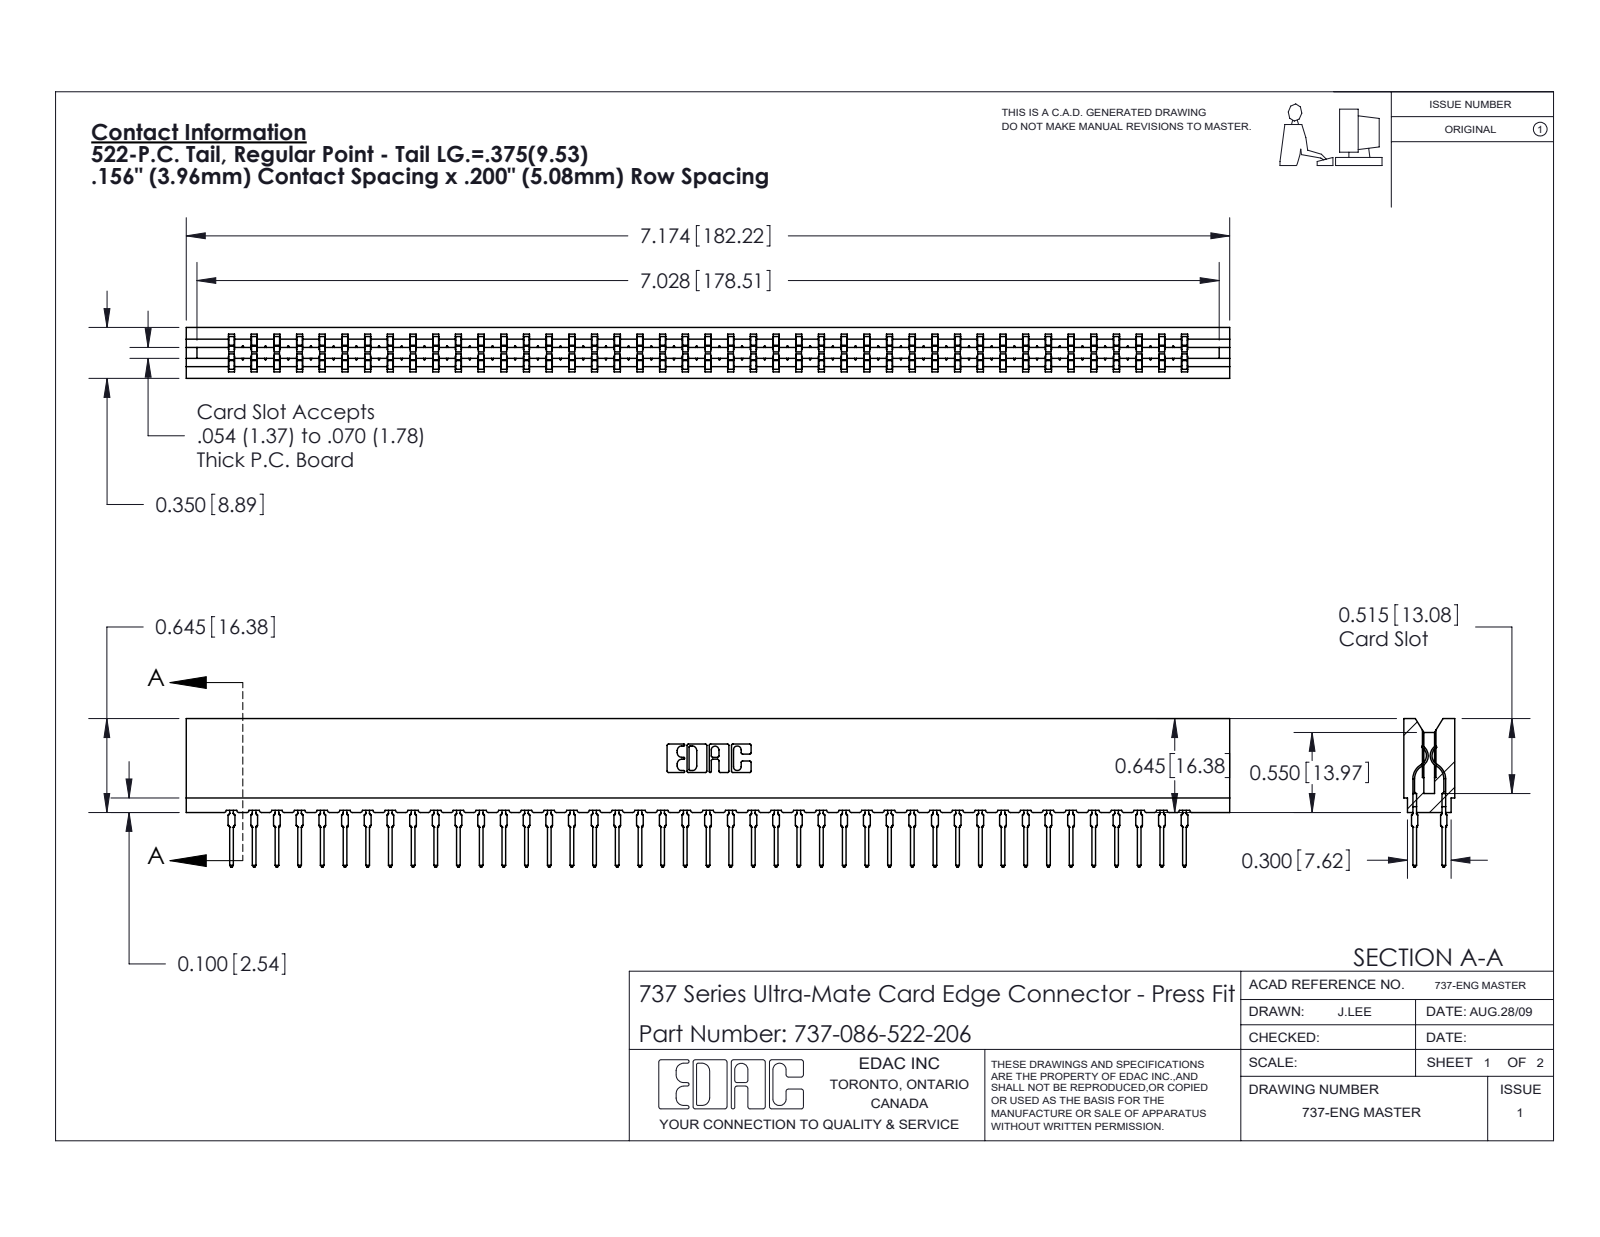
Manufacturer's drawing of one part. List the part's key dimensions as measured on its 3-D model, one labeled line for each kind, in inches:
Part name (STEP PRODUCT): 745-292-001_522; 737-086-522-206; 737 Part_Insulator Option - 06
STEP written by: SolidWorks 2020 (CONFIG_CONTROL_DESIGN)
Units: inches
Bodies: 87 solids, 7835 faces (4054 planar, 1545 cylindrical, 2236 other)
Overall size (bounding box): 7.174 × 1.021 × 0.35
Volume: 1.103 in³ · Surface area: 41.29 in²
Partial cylindrical surfaces — rounded edges, fillets, slot ends (radius × count): R0.021 ×172, R0.015 ×86, R0.01 ×22, R0.005 ×8, R0.011 ×8, R0.007 ×6, R0.031 ×6, R0.026 ×3
Main face-to-face distances: 0.138, 0.212, 0.35, 0.063, 0.287, 0.076, 0.149, 0.074, 0.045, 0.305
